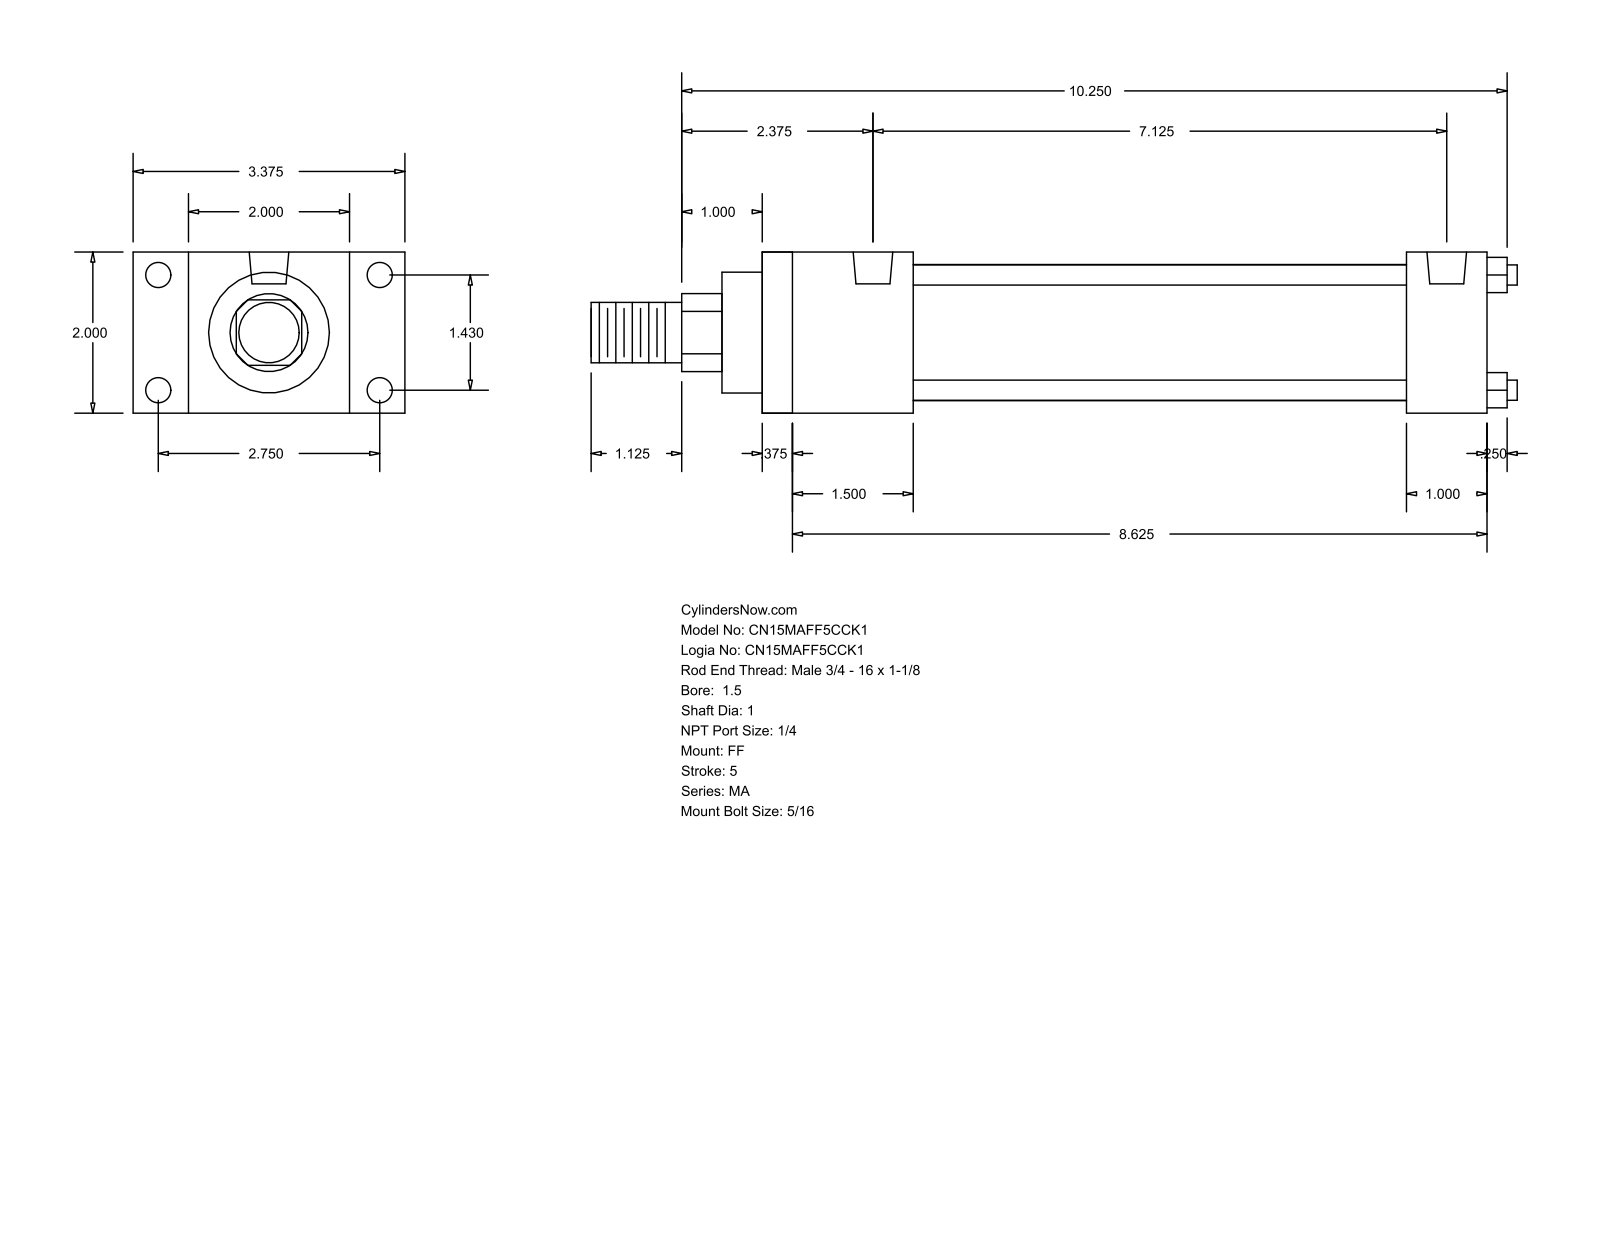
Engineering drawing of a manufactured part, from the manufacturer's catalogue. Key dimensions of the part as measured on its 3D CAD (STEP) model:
Part name (STEP PRODUCT): MA_FF__0150_1
STEP written by: GSSL Pune (CONFIG_CONTROL_DESIGN)
Units: millimetres
Bodies: 0 solids, 92 faces (64 planar, 28 cylindrical, 0 other)
Overall size (bounding box): 292.1 × 85.72 × 50.8
Round holes (diameter × count): ⌀7.94 ×8, ⌀12.49 ×2
Round bosses / shafts (diameter × count): ⌀6.35 ×4, ⌀42.93 ×1, ⌀38.1 ×1, ⌀25.4 ×1, ⌀19.05 ×1
Partial cylindrical surfaces — rounded edges, fillets, slot ends (radius × count): R12.29 ×1
Main face-to-face distances: 50.8, 228.6, 9.52, 219.08, 25.4, 47.63, 203.2, 38.11, 193.68, 155.57
Hole centre spacings: 36.32, 69.84, 78.72, 180.97
